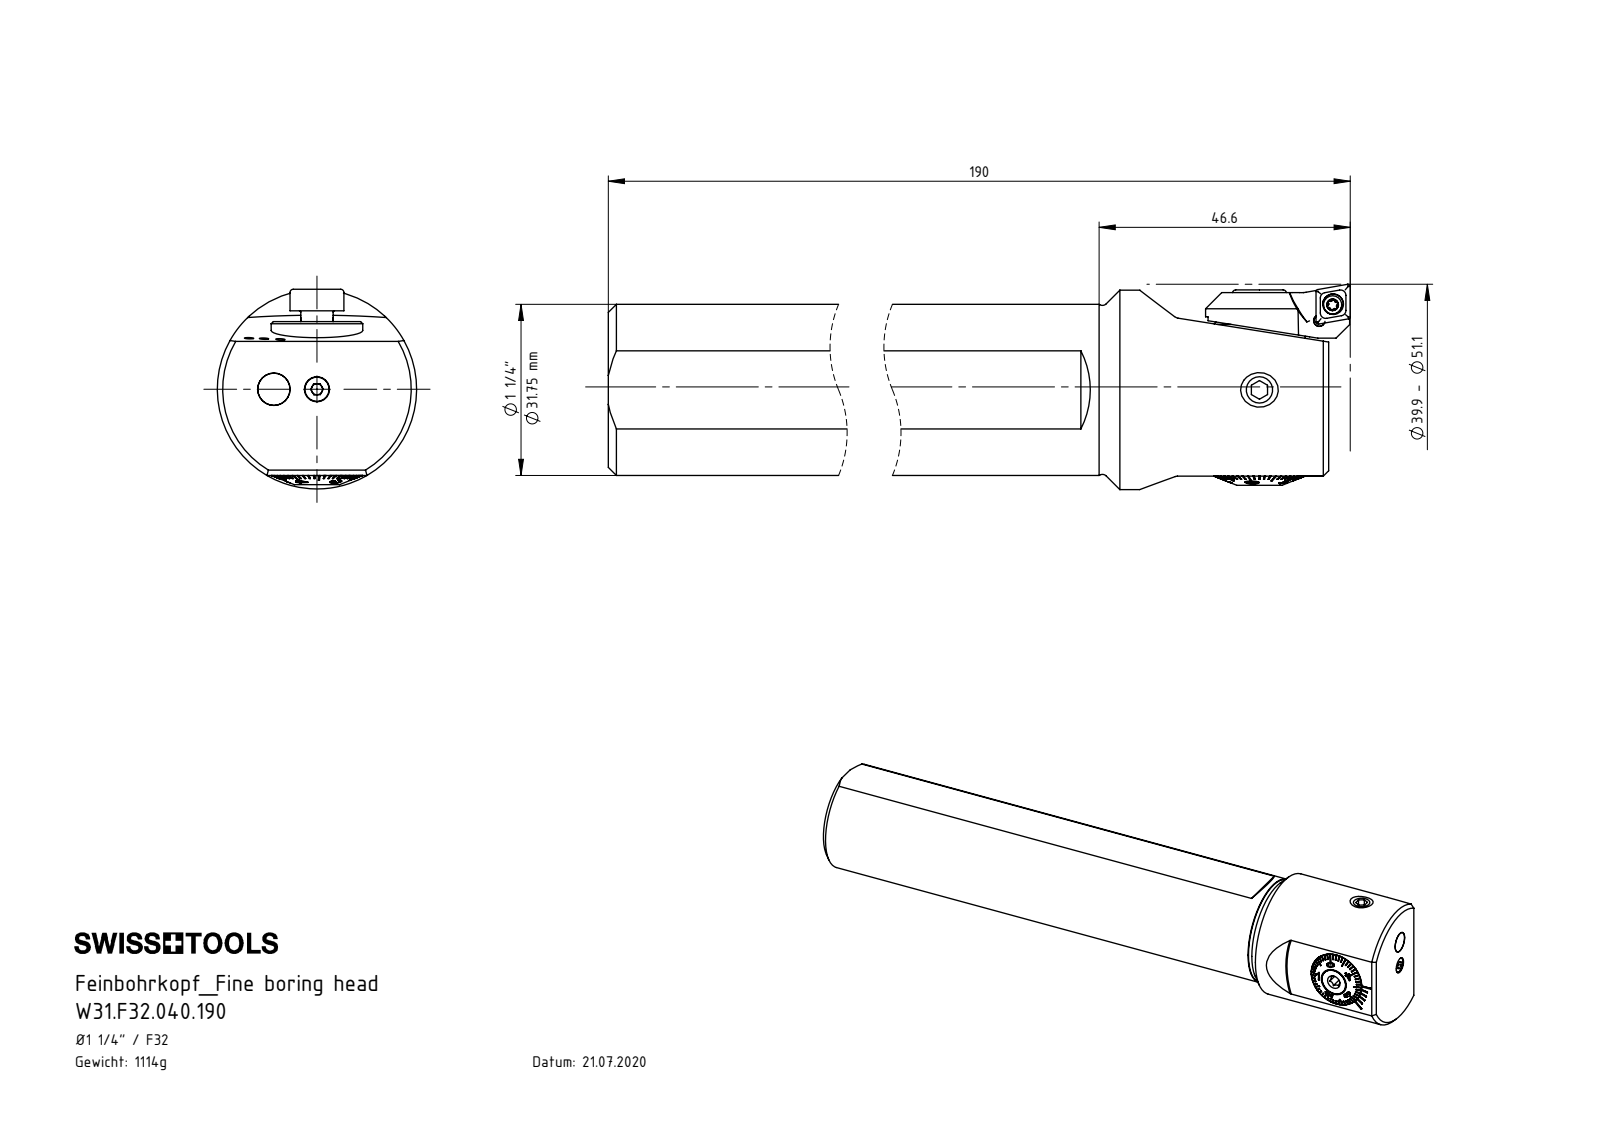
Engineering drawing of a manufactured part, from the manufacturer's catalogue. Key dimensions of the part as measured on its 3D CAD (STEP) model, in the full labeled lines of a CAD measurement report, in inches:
Part name (STEP PRODUCT): F32-BG1.010.006_A; ISO 4026 - M6 x 8; F32-BG1.AA4.017_Standart; W31.F32.040.190 (+8 more)
STEP written by: SolidWorks 2022 (CONFIG_CONTROL_DESIGN)
Units: inches
Bodies: 13 solids, 654 faces (301 planar, 108 cylindrical, 245 other)
Overall size (bounding box): 7.323 × 1.459 × 1.457
Volume: 8.609 in³ · Surface area: 51.68 in²
Round holes (diameter × count): ⌀0.059 ×3, ⌀0.13 ×2, ⌀0.197 ×2, ⌀0.335 ×2, ⌀0.081 ×1, ⌀0.106 ×1, ⌀0.114 ×1, ⌀0.118 ×1, ⌀0.165 ×1, ⌀0.236 ×1, ⌀0.276 ×1, ⌀0.291 ×1
Round bosses / shafts (diameter × count): ⌀0.236 ×2, ⌀1.457 ×1, ⌀1.25 ×1, ⌀0.669 ×1, ⌀0.669 ×1, ⌀0.663 ×1, ⌀0.577 ×1, ⌀0.394 ×1
Partial cylindrical surfaces — rounded edges, fillets, slot ends (radius × count): R0.055 ×4, R0.02 ×3, R0.069 ×2, R0.079 ×2, R0.126 ×1
Main face-to-face distances: 7.323, 0.177, 0.031, 0.146, 0.059, 0.947, 0.087, 0.091, 1.124, 1.033
Hole centre spacings: 0.315, 0.343
